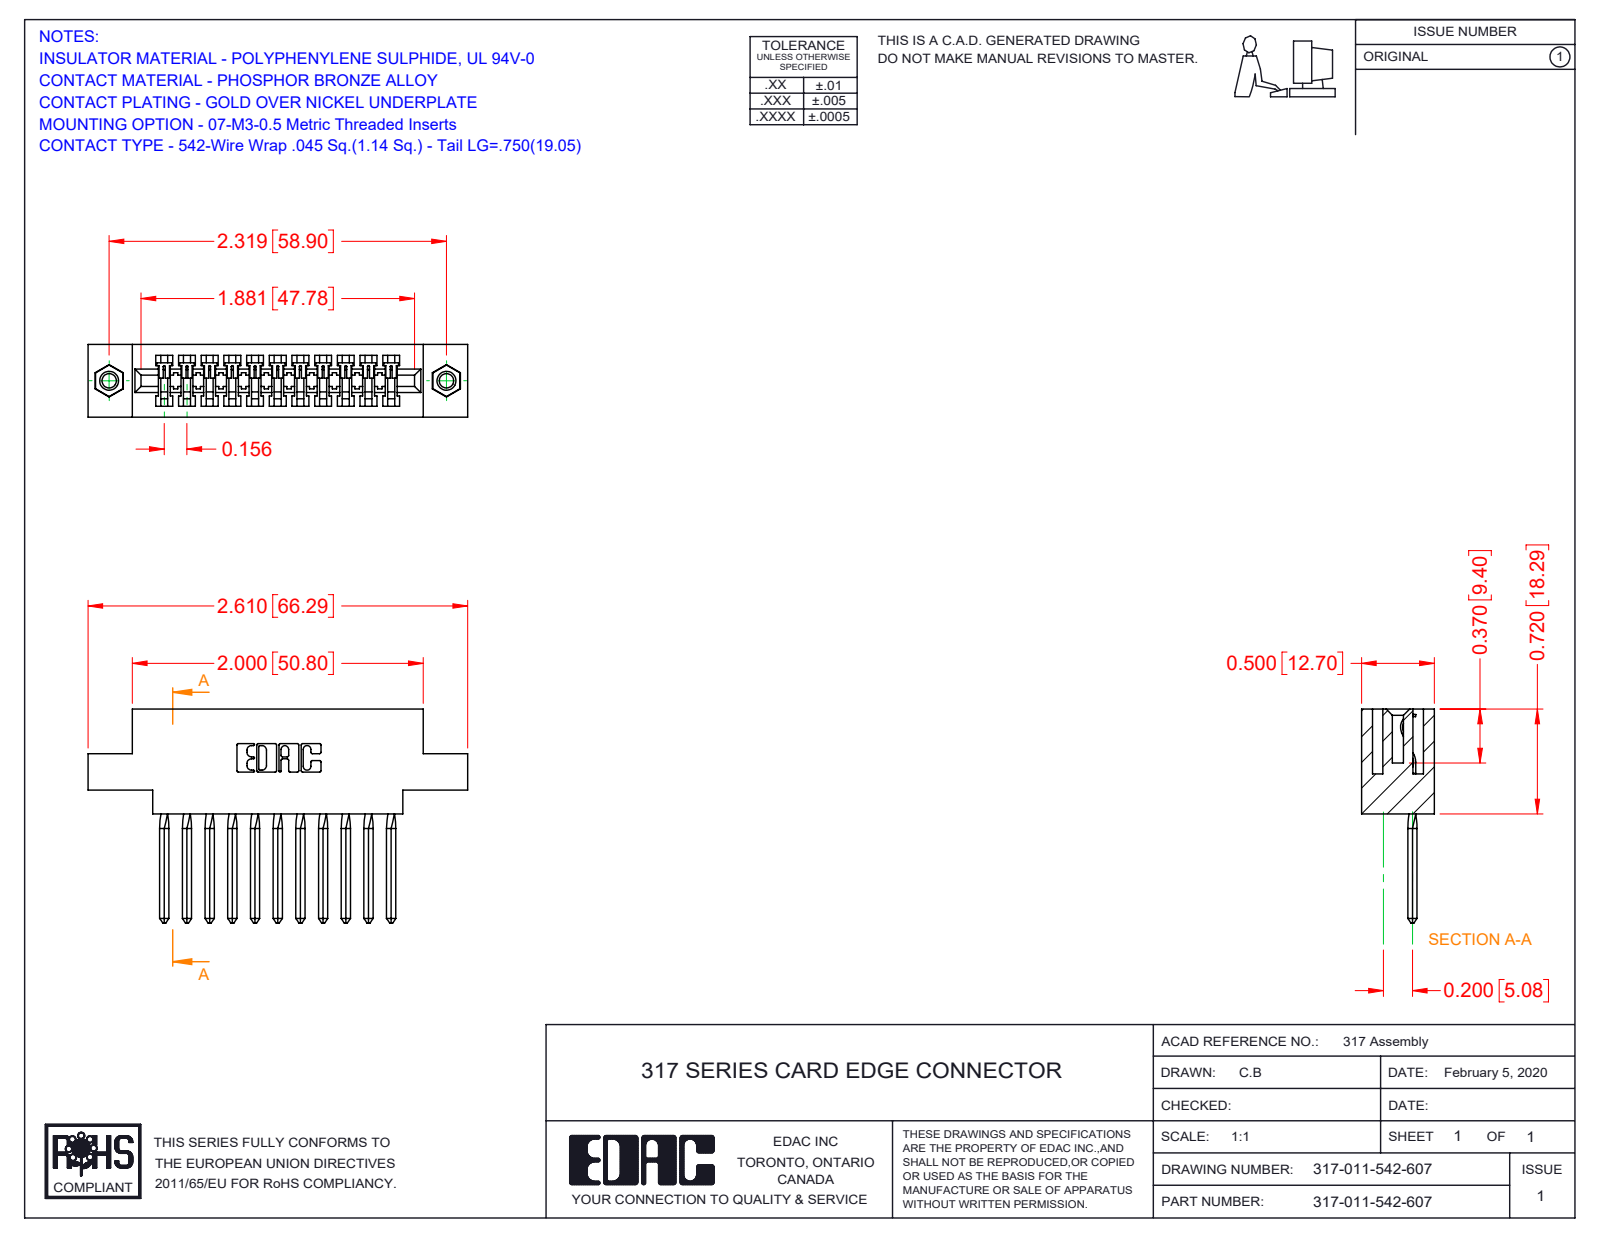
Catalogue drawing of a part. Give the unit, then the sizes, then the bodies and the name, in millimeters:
Units: millimetres
Overall size (bounding box): 66.3 × 37.3 × 12.7
Round holes (diameter × count): ⌀2.5 ×2, ⌀3.2 ×2, ⌀4 ×2
Round bosses / shafts (diameter × count): ⌀3.9 ×2
Partial cylindrical surfaces — rounded edges, fillets, slot ends (radius × count): R0.2 ×22, R0.3 ×22, R0.2 ×6, R0.8 ×6, R0.7 ×3, R1.9 ×1, R2.3 ×1, R2.5 ×1
Main face-to-face distances: 12.7, 1.9, 10.8, 2.8, 1.7, 5.6, 8.9, 3.5, 2.9, 8.4
Hole centre spacings: 58.9
Volume: 9 410 mm³ · Surface area: 10 810 mm²
Bodies: 14 solids, 987 faces (794 planar, 133 cylindrical, 60 other)
Part name (STEP PRODUCT): 317-011-542-607; 317 Part_.156 Dia - TI; 345-250-001_345-250-005-103; 317-290-003_542
STEP written by: SolidWorks 2016 (CONFIG_CONTROL_DESIGN)
